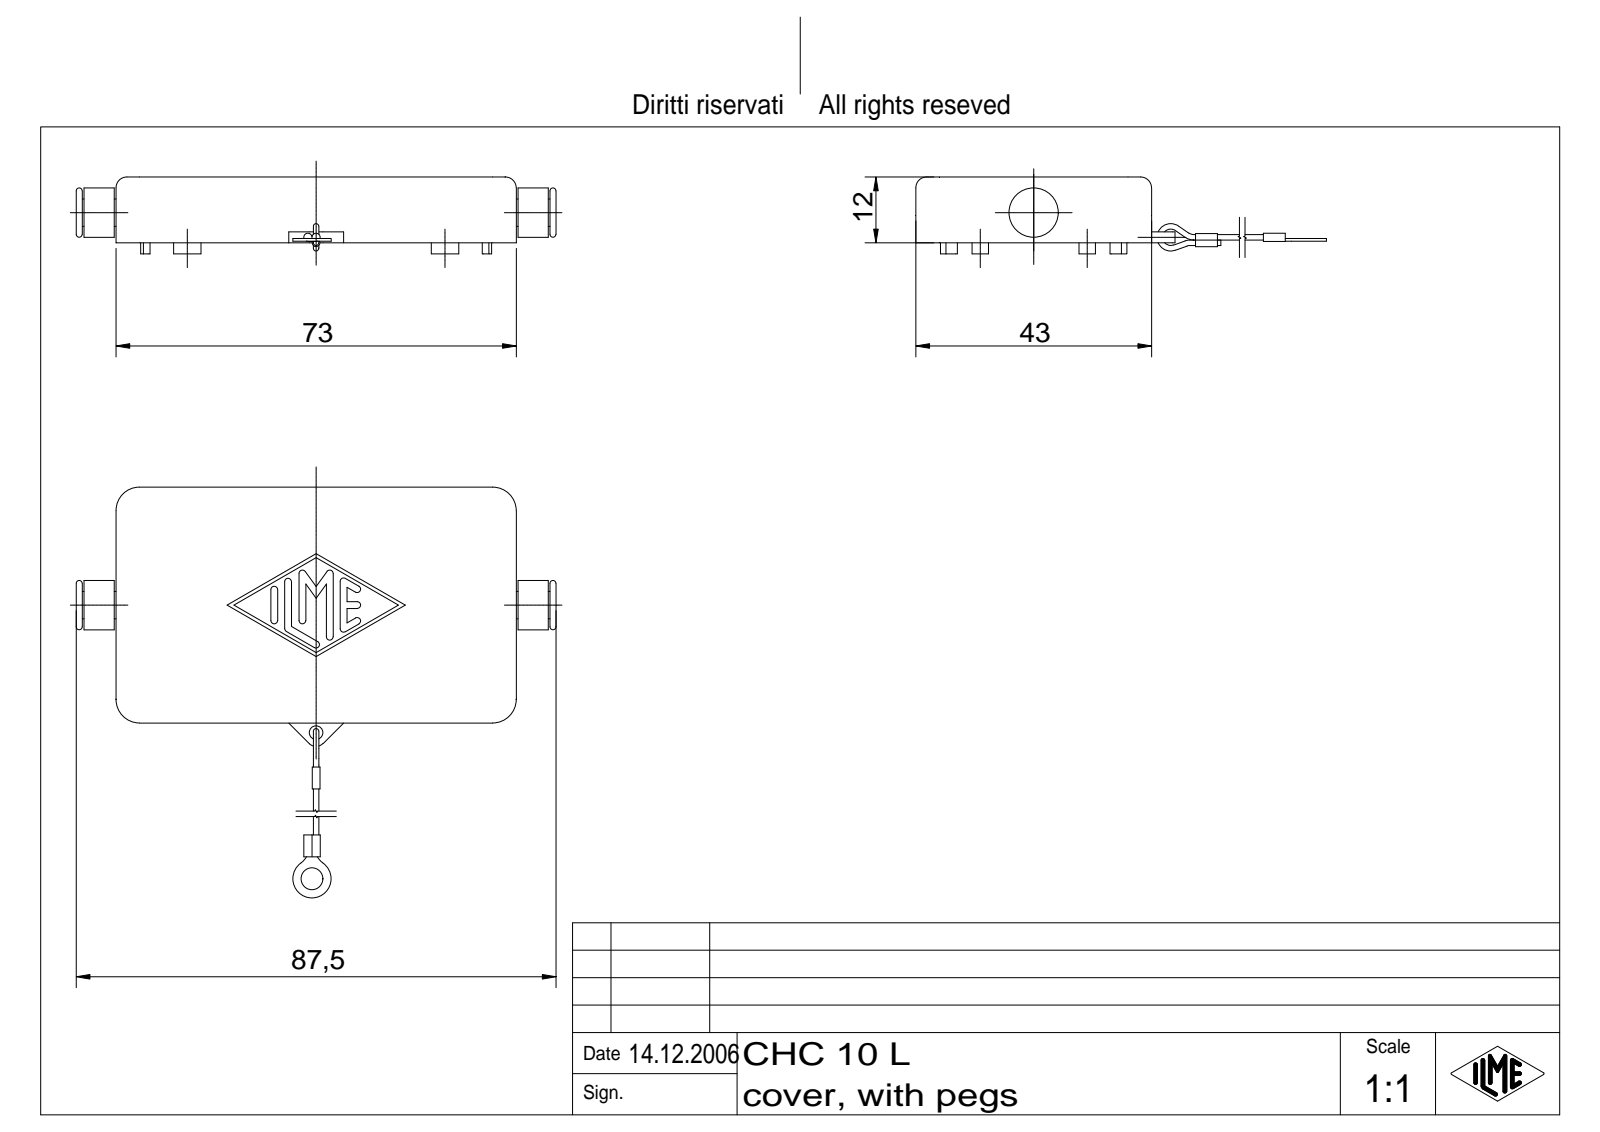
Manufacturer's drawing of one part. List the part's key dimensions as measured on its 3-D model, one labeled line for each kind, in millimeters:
Part name (STEP PRODUCT): CHC 10 L
STEP written by: Autodesk Inventor 7 (AUTOMOTIVE_DESIGN)
Units: millimetres
Bodies: 2 solids, 230 faces (95 planar, 75 cylindrical, 60 other)
Overall size (bounding box): 147.5 × 87.5 × 14
Volume: 19 361 mm³ · Surface area: 12 152 mm²
Round holes (diameter × count): ⌀2.5 ×1, ⌀4 ×1
Round bosses / shafts (diameter × count): ⌀1 ×4, ⌀9 ×1, ⌀7 ×1, ⌀5 ×1
Partial cylindrical surfaces — rounded edges, fillets, slot ends (radius × count): R0.62 ×14, R2 ×8, R0.7 ×4, R4.3 ×4, R0.75 ×2, R1 ×2, R3 ×2, R1.75 ×1
Main face-to-face distances: 3, 4.5, 12, 9, 38.5, 43, 34, 68.5, 73, 64
Hole centre spacings: 99.25
